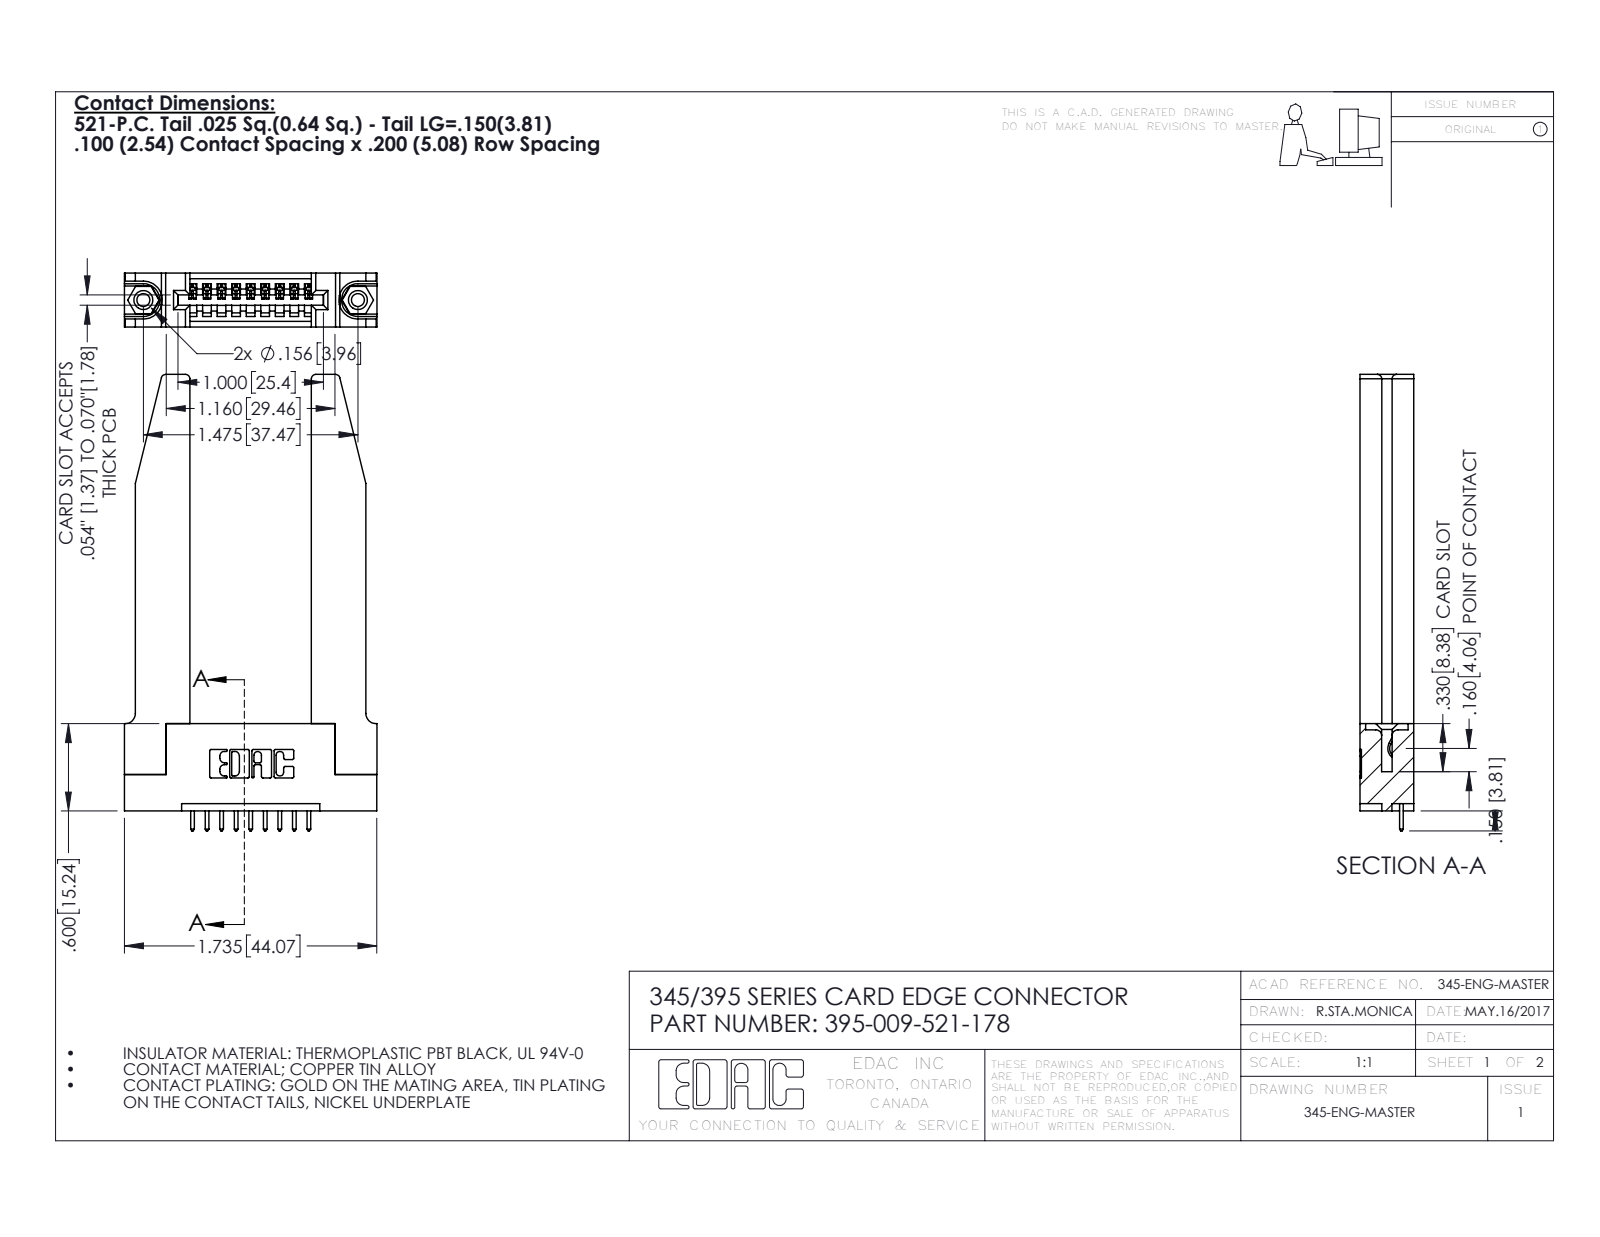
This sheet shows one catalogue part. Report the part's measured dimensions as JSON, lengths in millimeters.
{"part_name": "345-250-001_345-250-001-102; 345-292-001_345-293-121; 395-009-521-178; 345 Part_Flush Mounting Lugs - 0.156 Dia-TH (+1 more)", "step_written_by": "SolidWorks 2016 (CONFIG_CONTROL_DESIGN)", "units": "millimeters", "bodies": {"solids": 14, "faces": 882, "planar": 582, "cylindrical": 248, "other": 52}, "overall_size": [79.7, 44.1, 9.4], "volume_mm3": 11700, "surface_area_mm2": 11470, "round_holes": [[2.3, 2], [3.2, 2], [4, 2], [1.6, 1]], "round_bosses_or_shafts": [[3.9, 2]], "partial_cylinders_radius": [[0.3, 22], [0.2, 18], [0.3, 18], [0.8, 8], [0.2, 6], [0.8, 6], [0.7, 3], [0.8, 2]], "face_to_face_distances": [9.4, 1.8, 3.8, 7.6, 3.8, 5.6, 2, 21.2, 5.1, 2.4], "hole_center_spacings": [6.9, 31.6, 37.5]}
